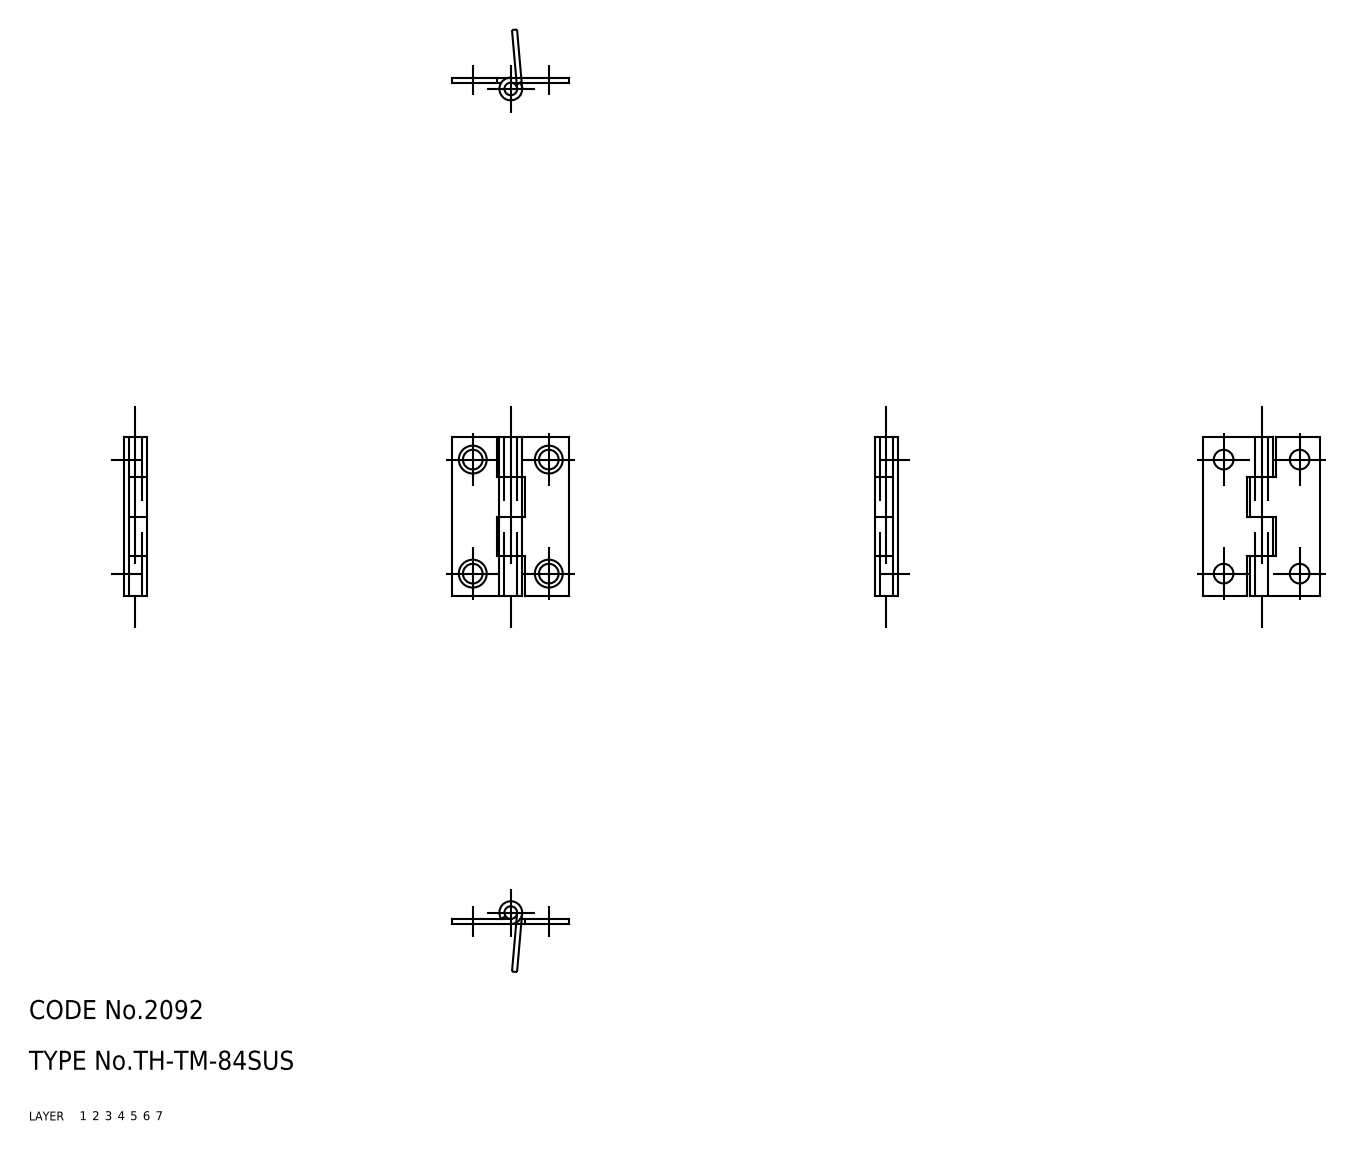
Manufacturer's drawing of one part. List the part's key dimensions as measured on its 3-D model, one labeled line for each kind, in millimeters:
Part name (STEP PRODUCT): shaft; hinge piece_B; hinge piece_A; TH_TM_84SUS_7722_36
STEP written by: CADfix (AUTOMOTIVE_DESIGN)
Units: millimetres
Bodies: 3 solids, 52 faces (0 planar, 0 cylindrical, 52 other)
Overall size (bounding box): 25 × 18.5 × 3.6
Volume: 518 mm³ · Surface area: 1 467 mm²
